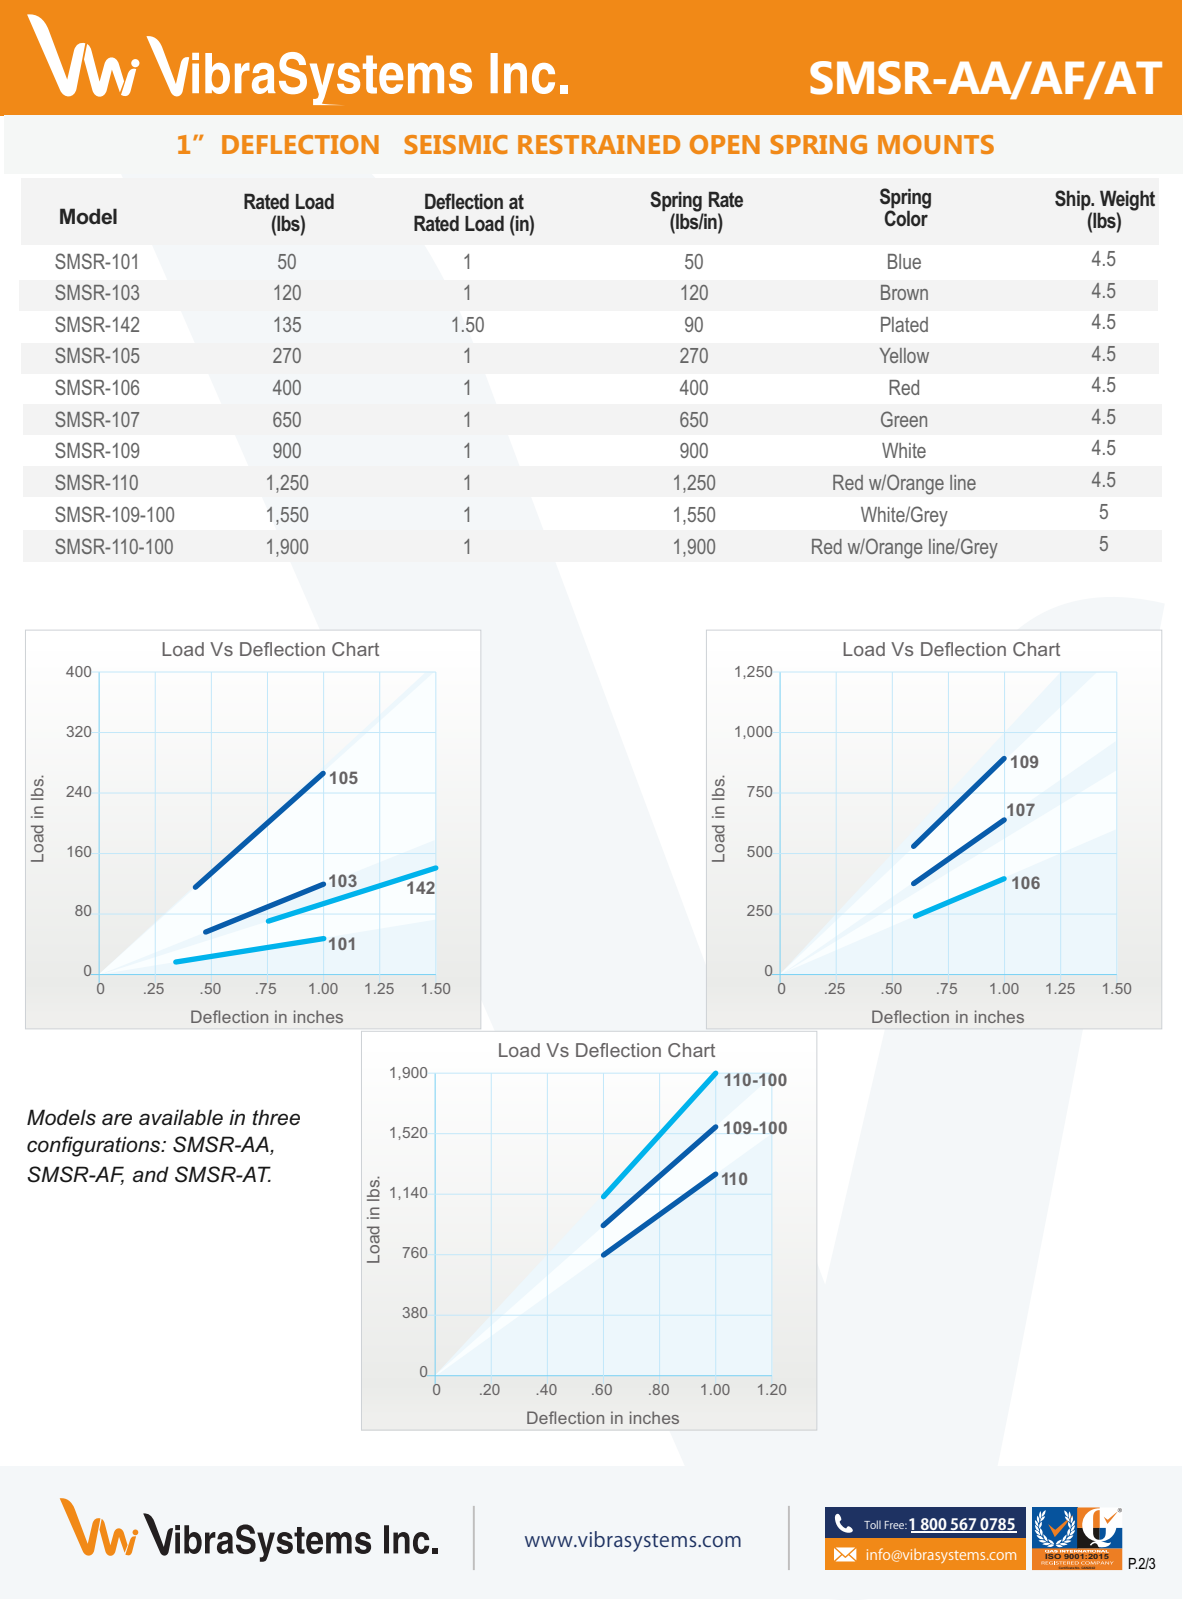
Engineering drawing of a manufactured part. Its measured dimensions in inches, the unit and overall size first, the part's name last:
Units: inches
Overall size (bounding box): 7 × 5.625 × 2.625
Round holes (diameter × count): ⌀0.437 ×3
Round bosses / shafts (diameter × count): ⌀1 ×3, ⌀0.375 ×2, ⌀2.18 ×1, ⌀2 ×1, ⌀1.125 ×1, ⌀1.125 ×1, ⌀0.375 ×1
Partial cylindrical surfaces — rounded edges, fillets, slot ends (radius × count): R0.25 ×12, R0.5 ×4, R0.062 ×2, R0.187 ×1, R0.375 ×1
Main face-to-face distances: 0.25, 2.625, 1.375, 1.125, 3.25, 2.875, 2.375, 4.375, 4.625, 4.187
Hole centre spacings: 3, 6
Volume: 23.3 in³ · Surface area: 130.5 in²
Bodies: 1 solid, 119 faces (59 planar, 52 cylindrical, 8 other)
Part name (STEP PRODUCT): SMSR-AA Rev J
STEP written by: SolidWorks 2016 (CONFIG_CONTROL_DESIGN)
